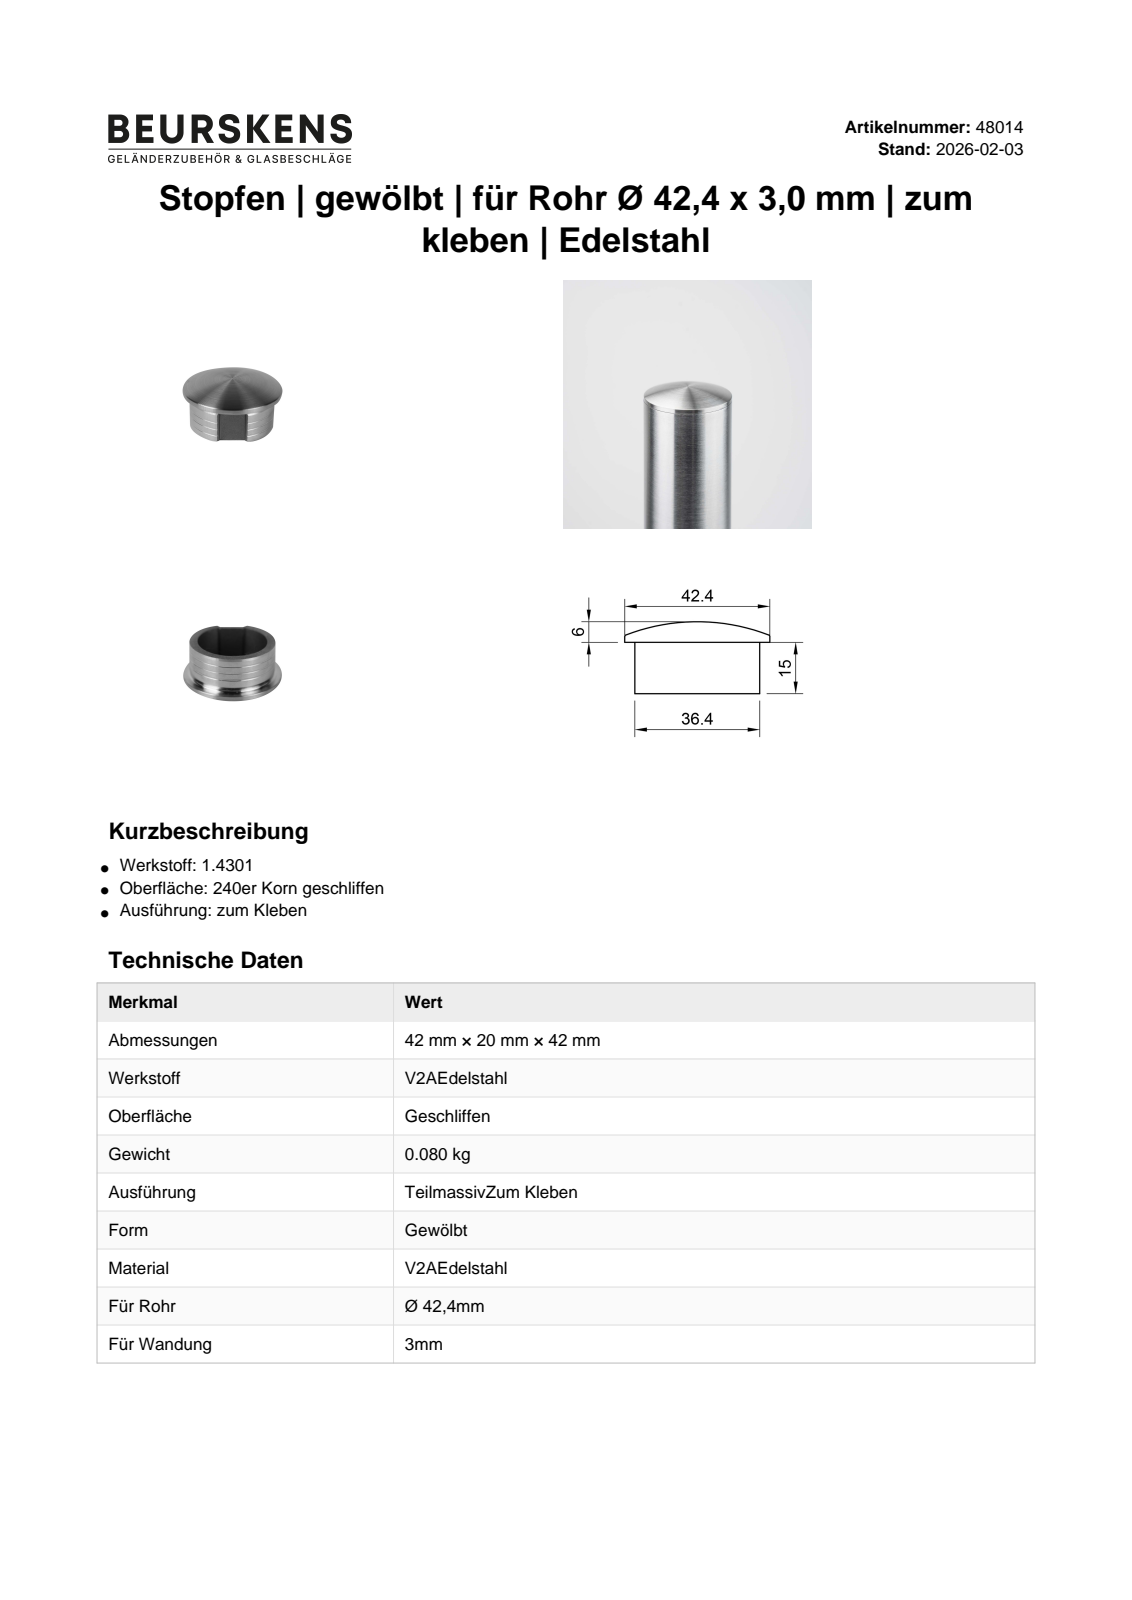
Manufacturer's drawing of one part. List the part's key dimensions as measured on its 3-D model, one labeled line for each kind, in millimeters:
Part name (STEP PRODUCT): 48014
STEP written by: Autodesk Inventor 2022 (AUTOMOTIVE_DESIGN)
Units: millimetres
Bodies: 1 solid, 12 faces (4 planar, 4 cylindrical, 4 other)
Overall size (bounding box): 42.4 × 42.4 × 21.01
Volume: 8 284 mm³ · Surface area: 6 982 mm²
Round holes (diameter × count): ⌀29 ×1, ⌀34.4 ×1
Round bosses / shafts (diameter × count): ⌀42.4 ×1, ⌀36.5 ×1
Main face-to-face distances: 15
